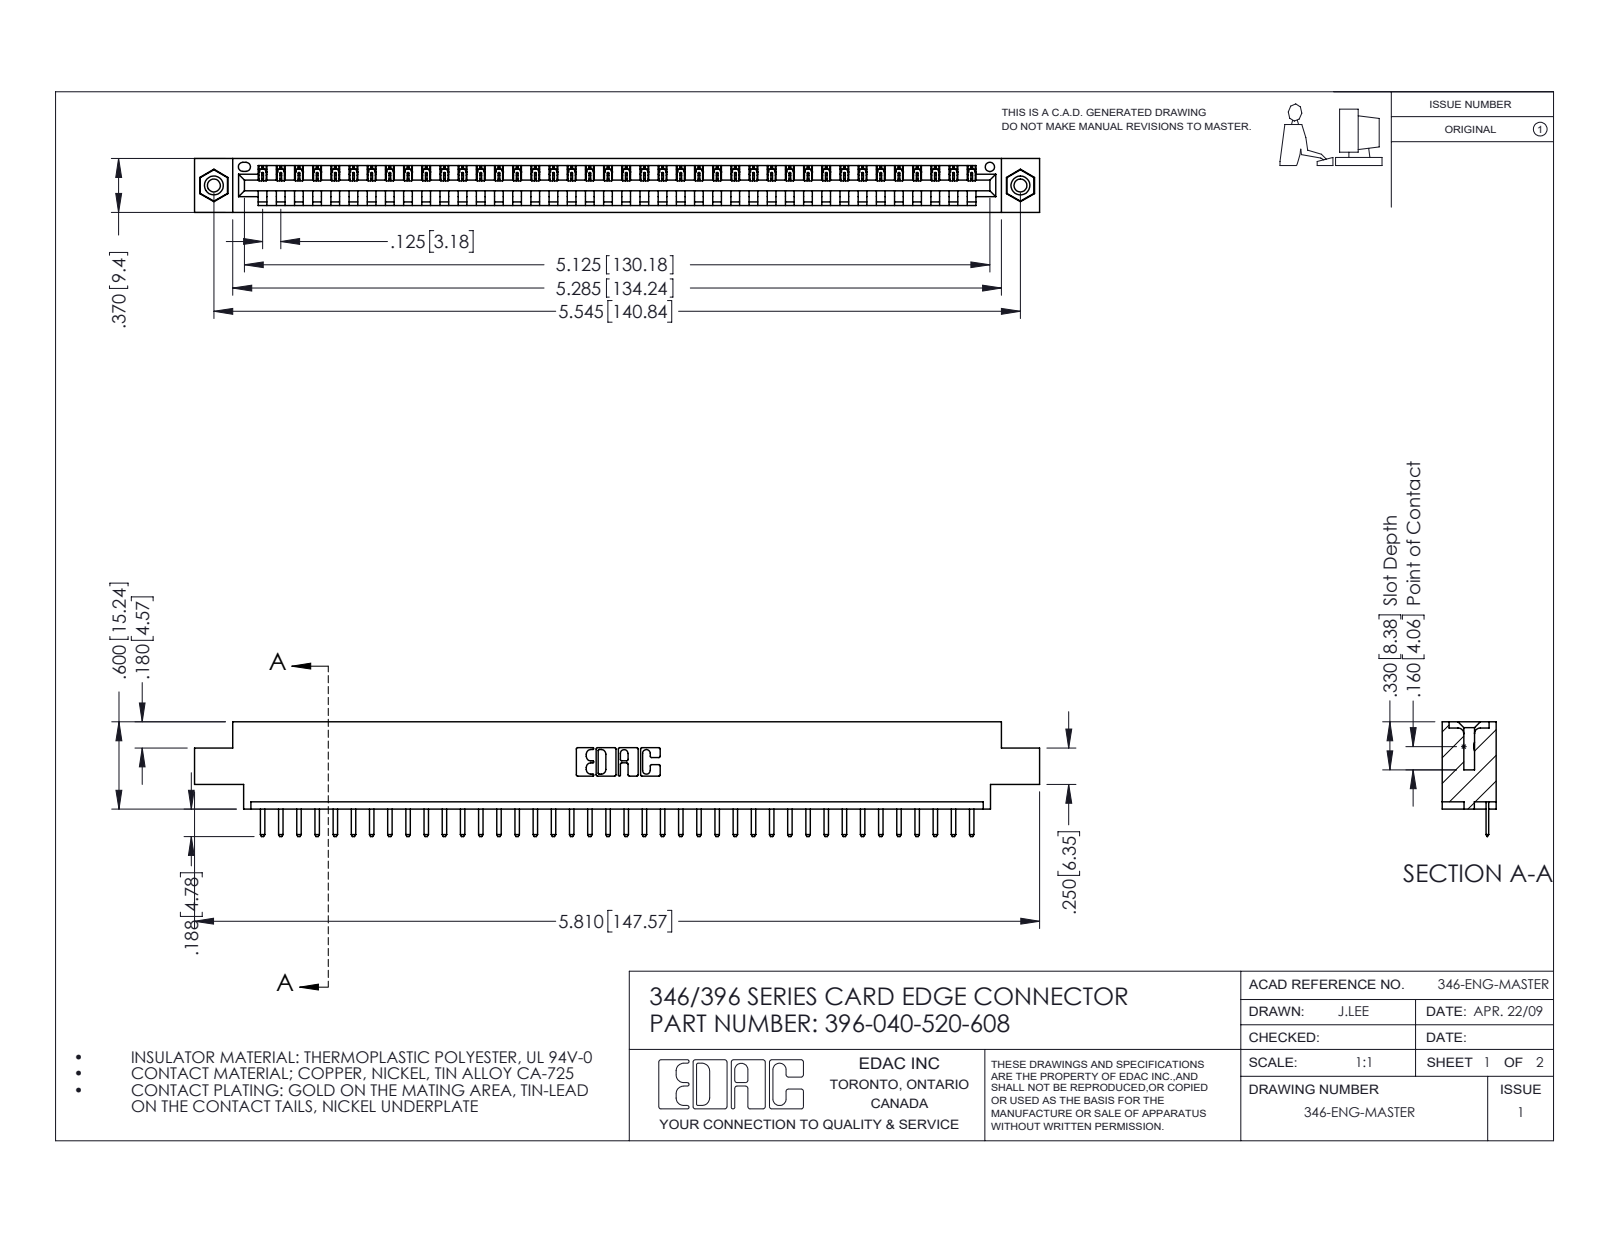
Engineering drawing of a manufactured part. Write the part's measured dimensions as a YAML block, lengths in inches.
part_name: "345-250-001_345-250-003-102; 345-292-001_345-293-120; 346 Part_0.170 Offset - 0.156 Dia-TI; 396-040-520-608"
step_written_by: "SolidWorks 2016 (CONFIG_CONTROL_DESIGN)"
units: inches
bodies: {solids: 43, faces: 2666, planar: 1792, cylindrical: 858, other: 16}
overall_size: [5.81, 0.788, 0.37]
volume: 0.844
surface_area: 26.46
round_holes:
  - {diameter: 0.089, count: 2}
  - {diameter: 0.125, count: 2}
  - {diameter: 0.156, count: 2}
  - {diameter: 0.064, count: 1}
round_bosses_or_shafts:
  - {diameter: 0.155, count: 2}
partial_cylinders:
  - {radius: 0.01, count: 82}
  - {radius: 0.006, count: 80}
  - {radius: 0.01, count: 22}
  - {radius: 0.007, count: 6}
  - {radius: 0.031, count: 6}
  - {radius: 0.026, count: 3}
  - {radius: 0.031, count: 2}
  - {radius: 0.04, count: 2}
face_to_face_distances: [0.048, 0.322, 0.37, 0.25, 0.222, 0.148, 0.1, 0.174, 0.072, 0.298]
hole_center_spacings: [0.246, 5.336, 5.545]
